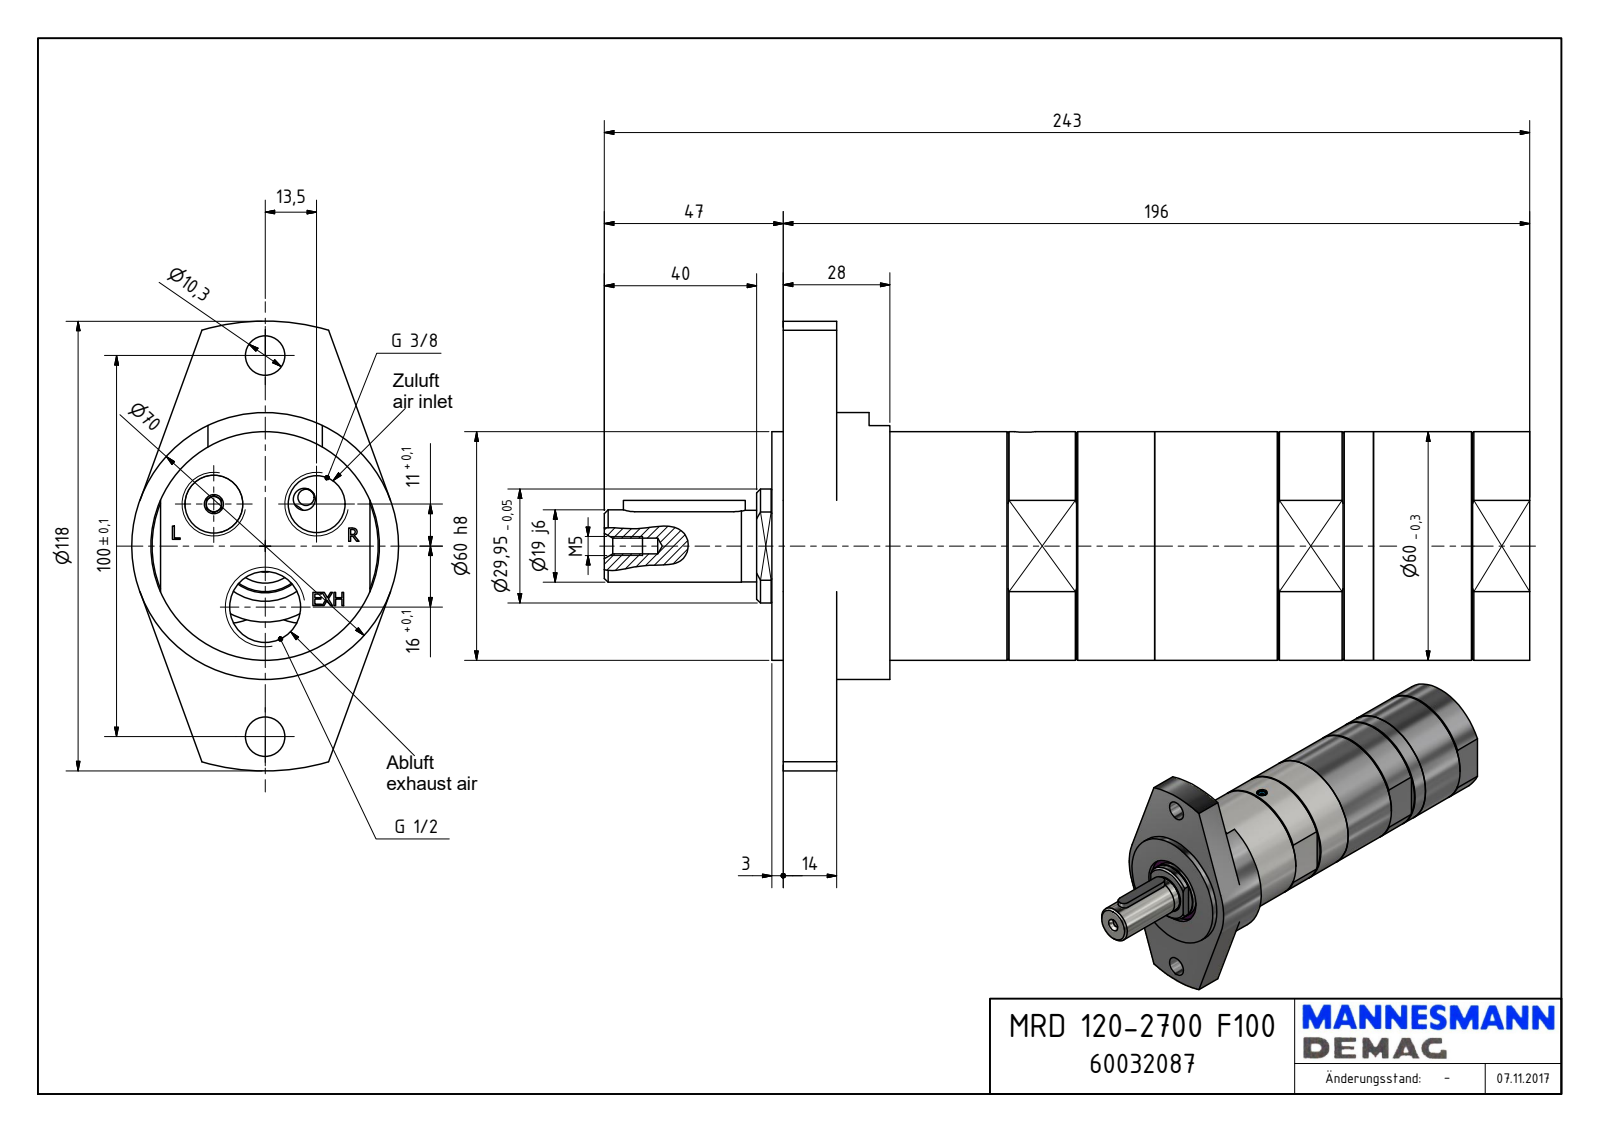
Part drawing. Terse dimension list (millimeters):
name: MRD 120-2700 F100_60032087
written by: Autodesk Inventor 2018 (AUTOMOTIVE_DESIGN)
unit: mm
bodies: 1 solid, 224 faces (131 planar, 50 cylindrical, 43 other)
size: 243 × 118 × 70
volume: 618 035 mm³; area: 63 016 mm²
holes: 2× ⌀4, 2× ⌀10.3, 2× ⌀14.95, 1× ⌀1.55, 1× ⌀4.13, 1× ⌀5.5, 1× ⌀18.63, 1× ⌀35, 1× ⌀53.38
bosses: 1× ⌀70, 1× ⌀60, 1× ⌀55.18, 1× ⌀53.18, 1× ⌀29.95, 1× ⌀19, 1× ⌀18.8, 1× ⌀5
rounds: 2× R3, 2× R7.5, 1× R8.5, 1× R19.29, 1× R23.5, 1× R25.82, 1× R59
face distances: 14, 196, 182, 3, 17, 199, 55, 28, 31, 168
hole spacings: 17.41, 30.19, 41.27, 50, 62.48, 16, 27, 34
